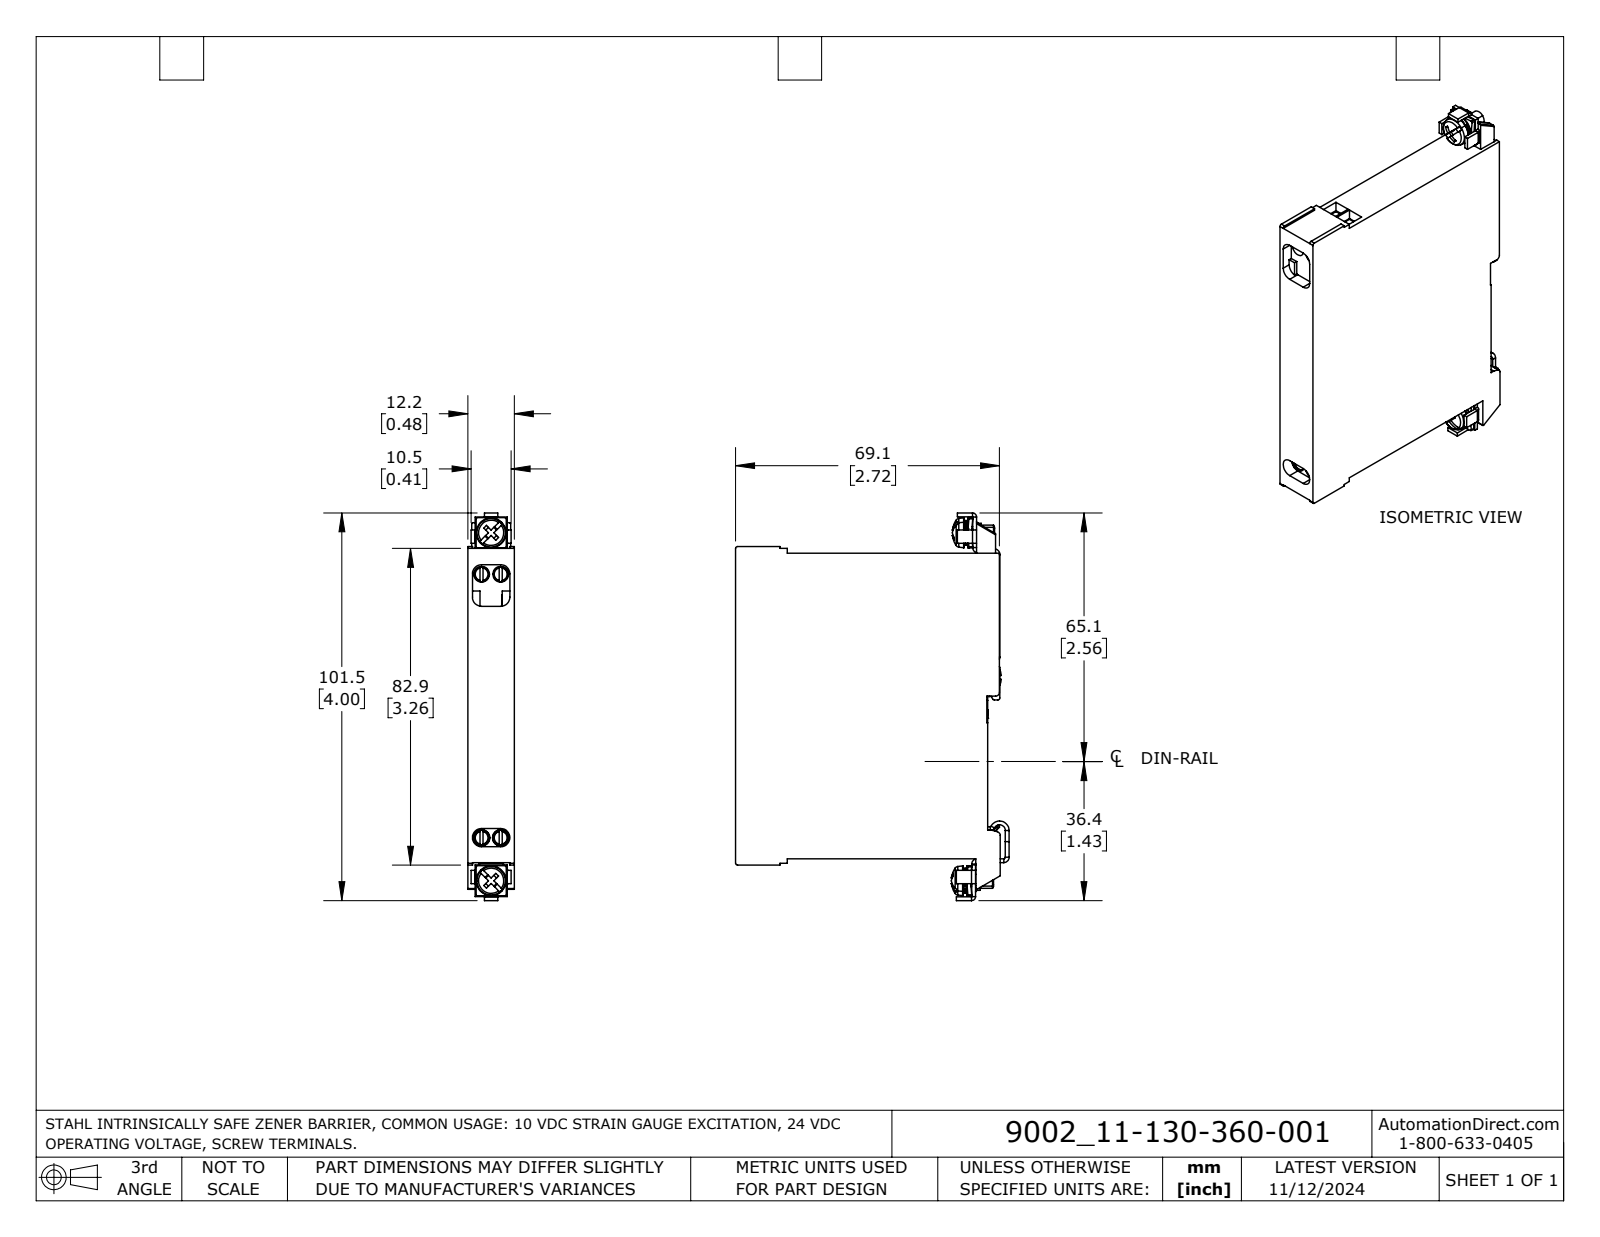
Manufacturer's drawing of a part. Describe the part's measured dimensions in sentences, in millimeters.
The part is named "900211-130-360-001". Its 3-D file was written by "SolidWorks 2023 (AUTOMOTIVE_DESIGN)". It is 4 solids with 762 faces: 528 planar, 146 cylindrical and 88 other. Overall it measures 101.5 by 71.6 by 12.2 millimeters. Its volume is 65 250 cubic millimeters and its surface area 21 750 square millimeters. Round holes: 4 of diameter 4.1, 3 of diameter 4.3, 2 of diameter 3.3, 2 of diameter 4.2, 1 of diameter 3. Round bosses or shafts: 3 of diameter 7.8, 3 of diameter 4, 2 of diameter 5, 2 of diameter 3.1, 1 of diameter 6.5. Partial cylindrical surfaces (rounded edges, fillets, slot ends): 16 of radius 0.5, 8 of radius 0.3, 6 of radius 0.4, 6 of radius 1, 6 of radius 1, 6 of radius 1.4, 6 of radius 2.4, 4 of radius 0.3. The main face-to-face distances are 12.2, 1, 79, 1.1, 2, 78, 2.2, 80, 2.1, 1.2. The hole center spacings are 5, 11.1, 11.5, 27.1, 28.2, 41, 42.1, 69.
